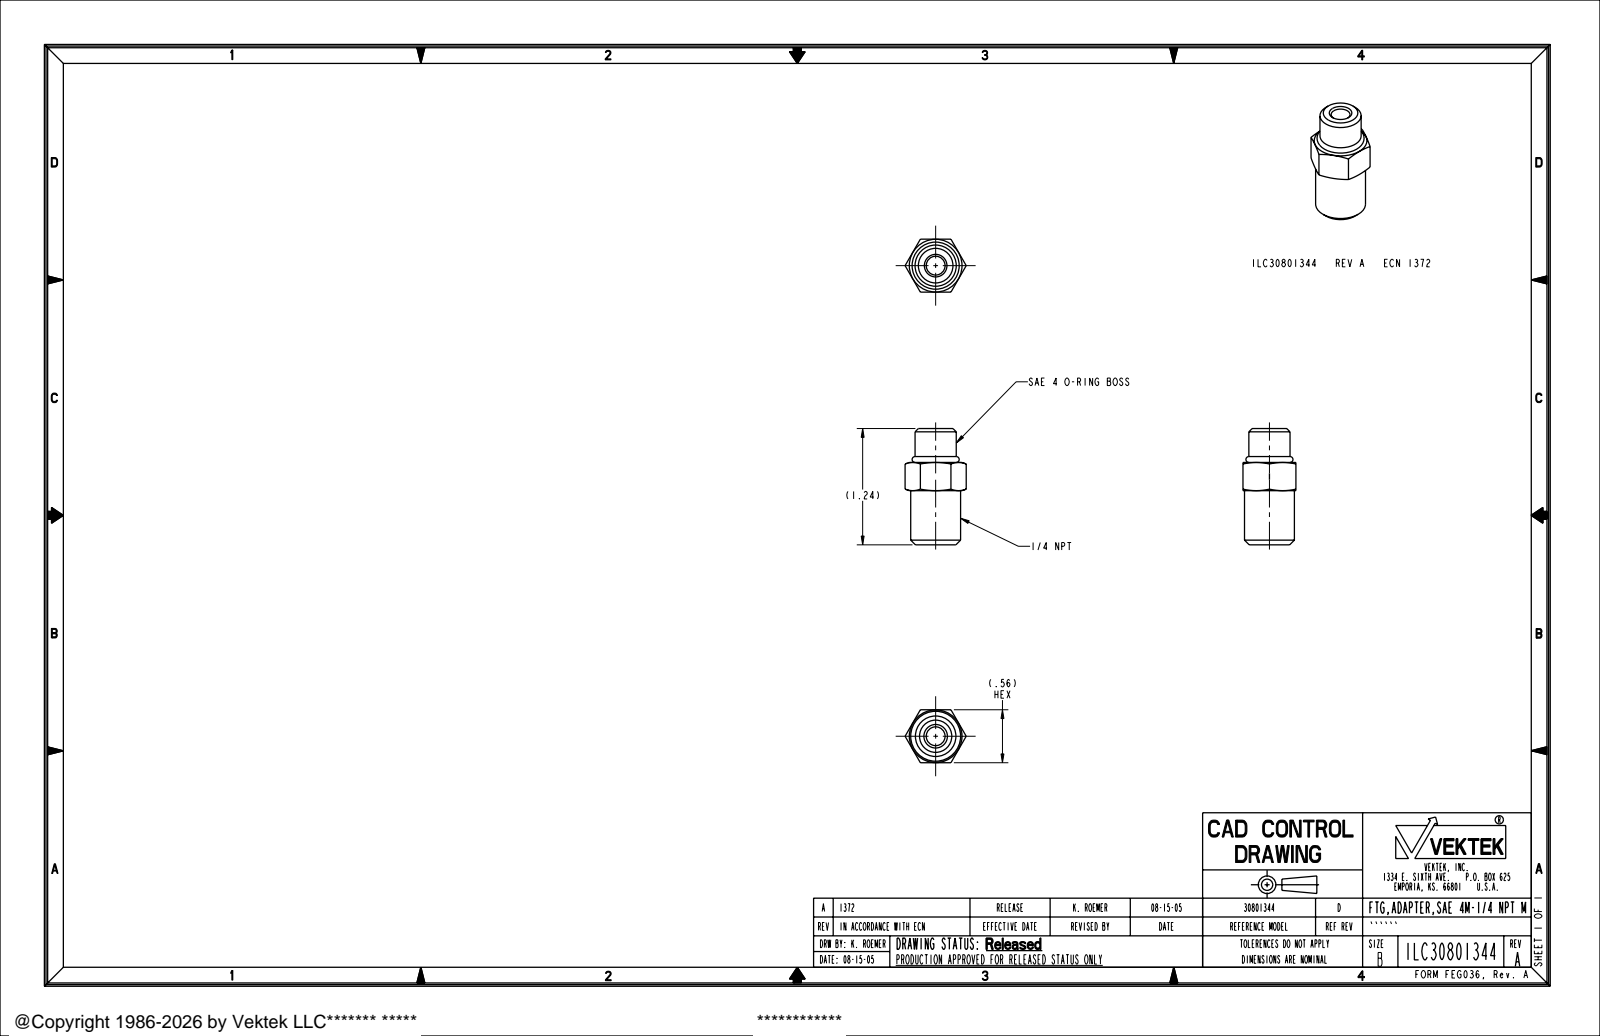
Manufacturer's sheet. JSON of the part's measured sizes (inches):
{"part_name": "ILC30801344", "step_written_by": "PRO/ENGINEER BY PARAMETRIC TECHNOLOGY CORPORATION, 2004290 (AUTOMOTIVE_DESIGN_CC2)", "units": "inches", "bodies": {"solids": 1, "faces": 33, "planar": 11, "cylindrical": 8, "other": 14}, "overall_size": [1.235, 0.65, 0.563], "volume_in3": 0.209, "surface_area_in2": 3.349, "round_holes": [[0.2, 1], [0.25, 1]], "round_bosses_or_shafts": [[0.53, 1], [0.437, 1]], "face_to_face_distances": [0.562, 0.36, 0.875, 1.235, 0.575, 0.3, 0.66, 0.75, 0.175, 0.125]}
